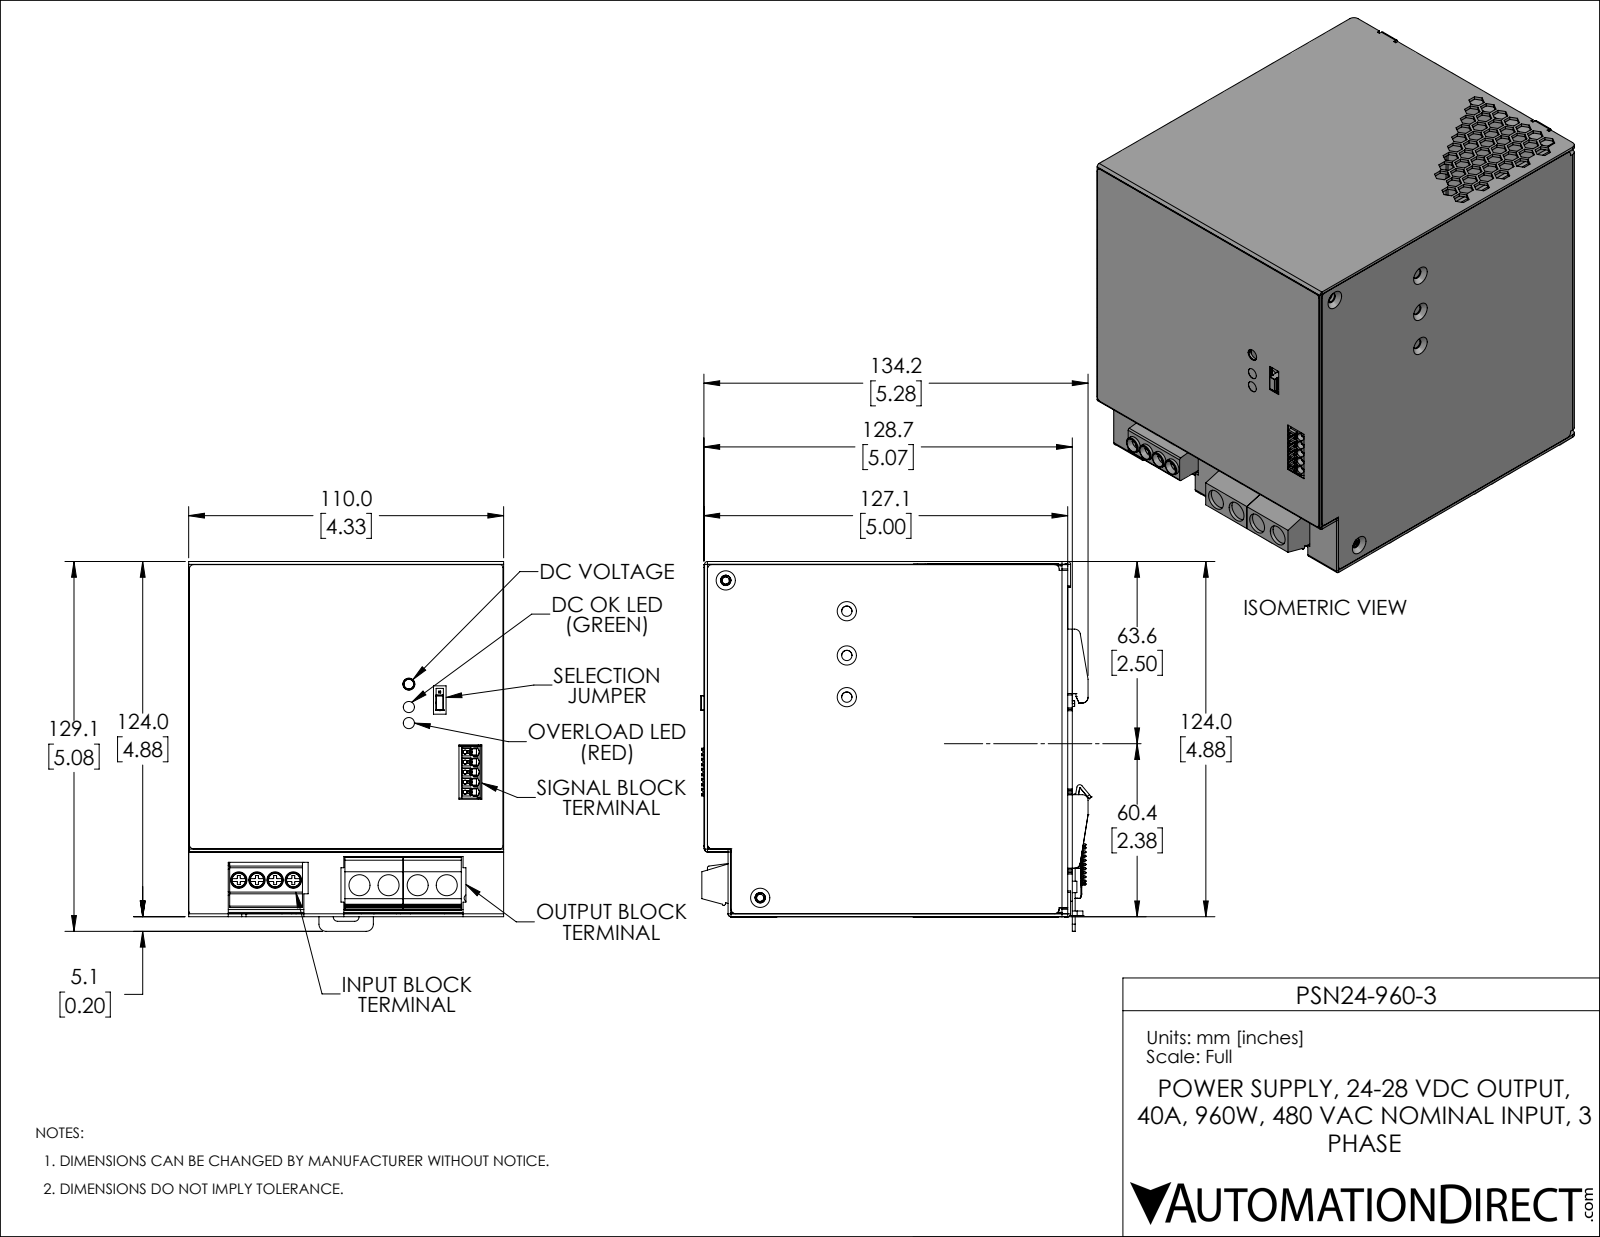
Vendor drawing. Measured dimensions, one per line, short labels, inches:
name: PSN24-960-3
written by: SolidWorks 2019 (AUTOMOTIVE_DESIGN)
unit: in
bodies: 23 solids, 2618 faces (2011 planar, 515 cylindrical, 92 other)
size: 5.399 × 5.083 × 4.333
volume: 13.09 in³; area: 386.5 in²
holes: 9× ⌀0.142, 9× ⌀0.157, 8× ⌀0.098, 7× ⌀0.118, 5× ⌀0.055, 4× ⌀0.193, 4× ⌀0.289, 3× ⌀0.063, 2× ⌀0.154, 1× ⌀0.138, 1× ⌀0.165
bosses: 4× ⌀0.226, 4× ⌀0.185, 4× ⌀0.157, 2× ⌀0.118, 2× ⌀0.079, 2× ⌀0.02, 1× ⌀0.134
rounds: 117× R0.02, 28× R0.004, 26× R0.059, 21× R0.008, 21× R0.039, 16× R0.012, 14× R0.079, 13× R0.063
face distances: 0.079, 0.039, 4.252, 4.843, 4.914, 4.331, 4.173, 0.079, 4.993, 4.954
hole spacings: 0.138, 0.194, 0.276, 0.307, 0.136, 0.413, 0.435, 0.25
